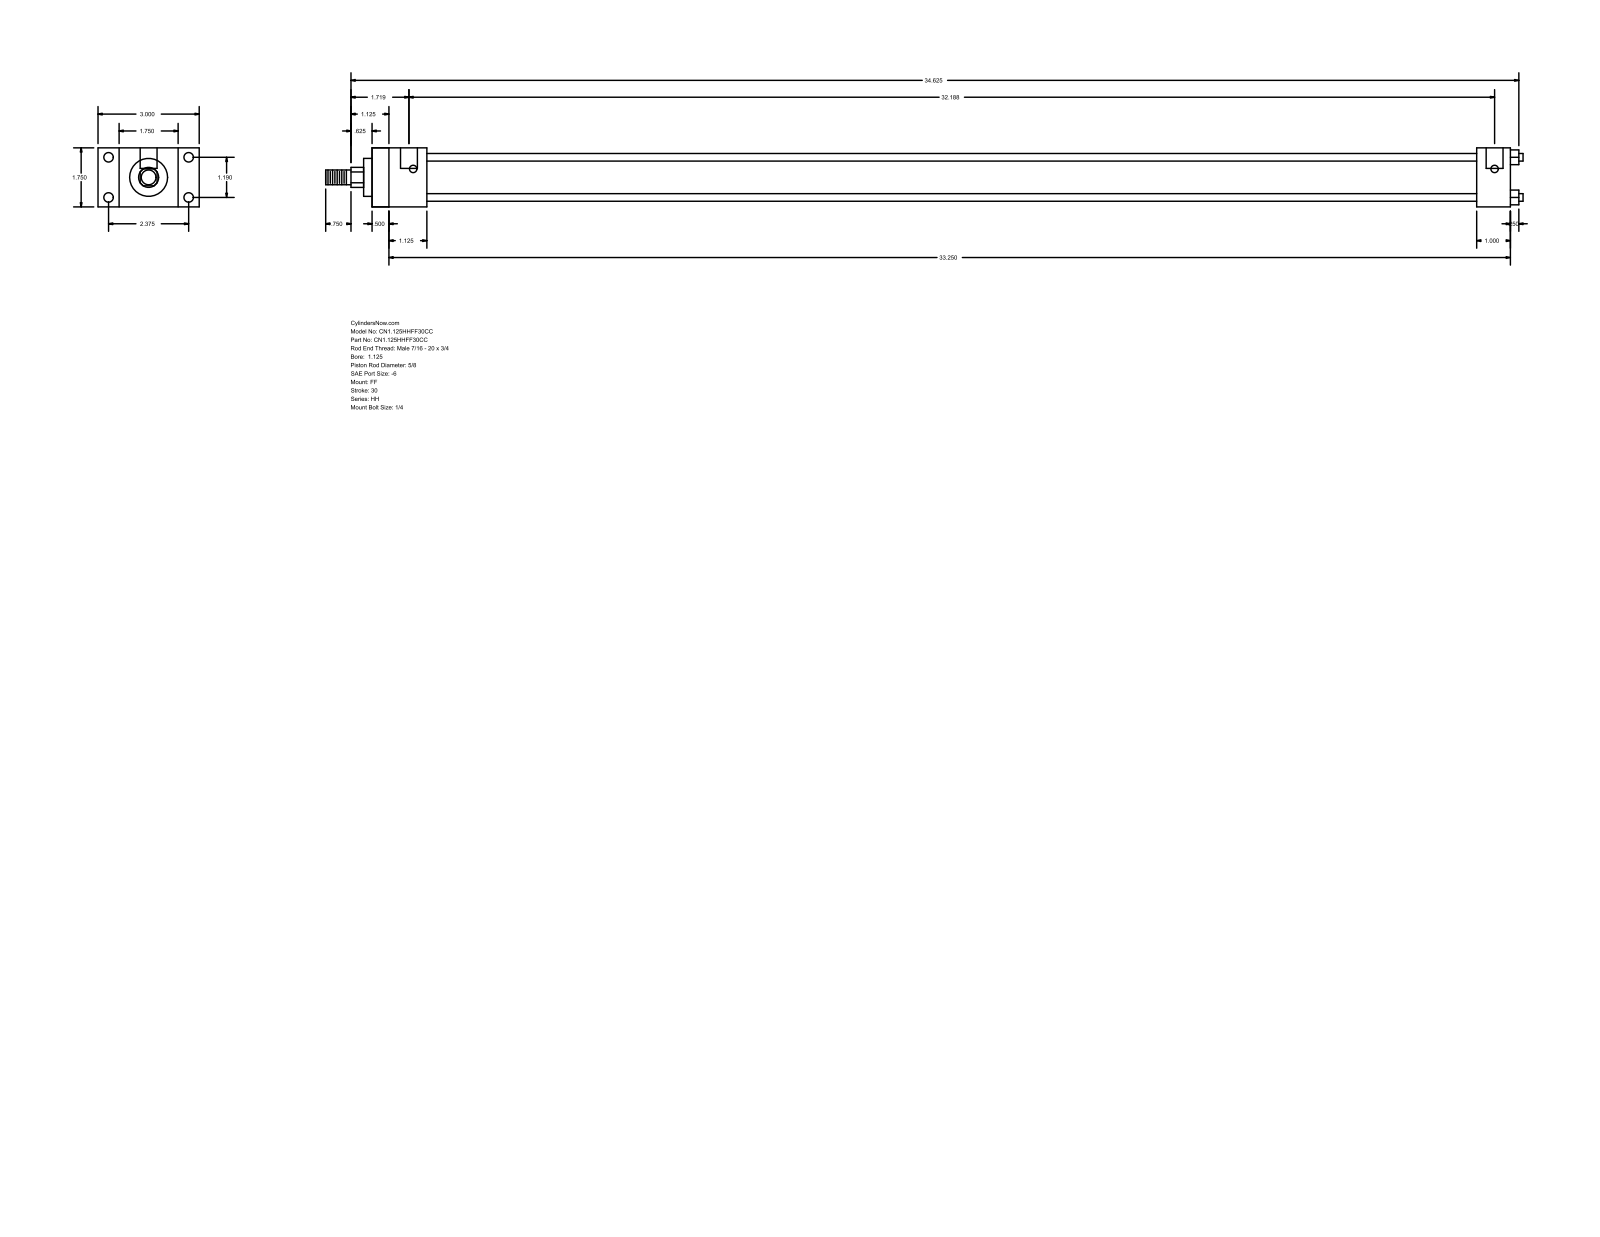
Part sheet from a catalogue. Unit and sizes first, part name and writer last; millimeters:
Units: millimetres
Overall size (bounding box): 901.7 × 76.2 × 44.45
Round holes (diameter × count): ⌀5.56 ×4, ⌀7.14 ×4, ⌀12.7 ×2
Round bosses / shafts (diameter × count): ⌀5.71 ×4, ⌀34.92 ×1, ⌀28.57 ×1, ⌀15.88 ×1, ⌀11.11 ×1
Partial cylindrical surfaces — rounded edges, fillets, slot ends (radius × count): R7.54 ×1
Main face-to-face distances: 44.46, 857.24, 12.69, 844.55, 15.87, 28.58, 60.33, 41.27, 831.85, 819.16
Hole centre spacings: 30.22, 60.32, 67.47, 814.39, 3.17, 817.56
Bodies: 0 solids, 92 faces (64 planar, 28 cylindrical, 0 other)
Part name (STEP PRODUCT): HH_FF__0112_0.625
STEP written by: GSSL Pune (CONFIG_CONTROL_DESIGN)
